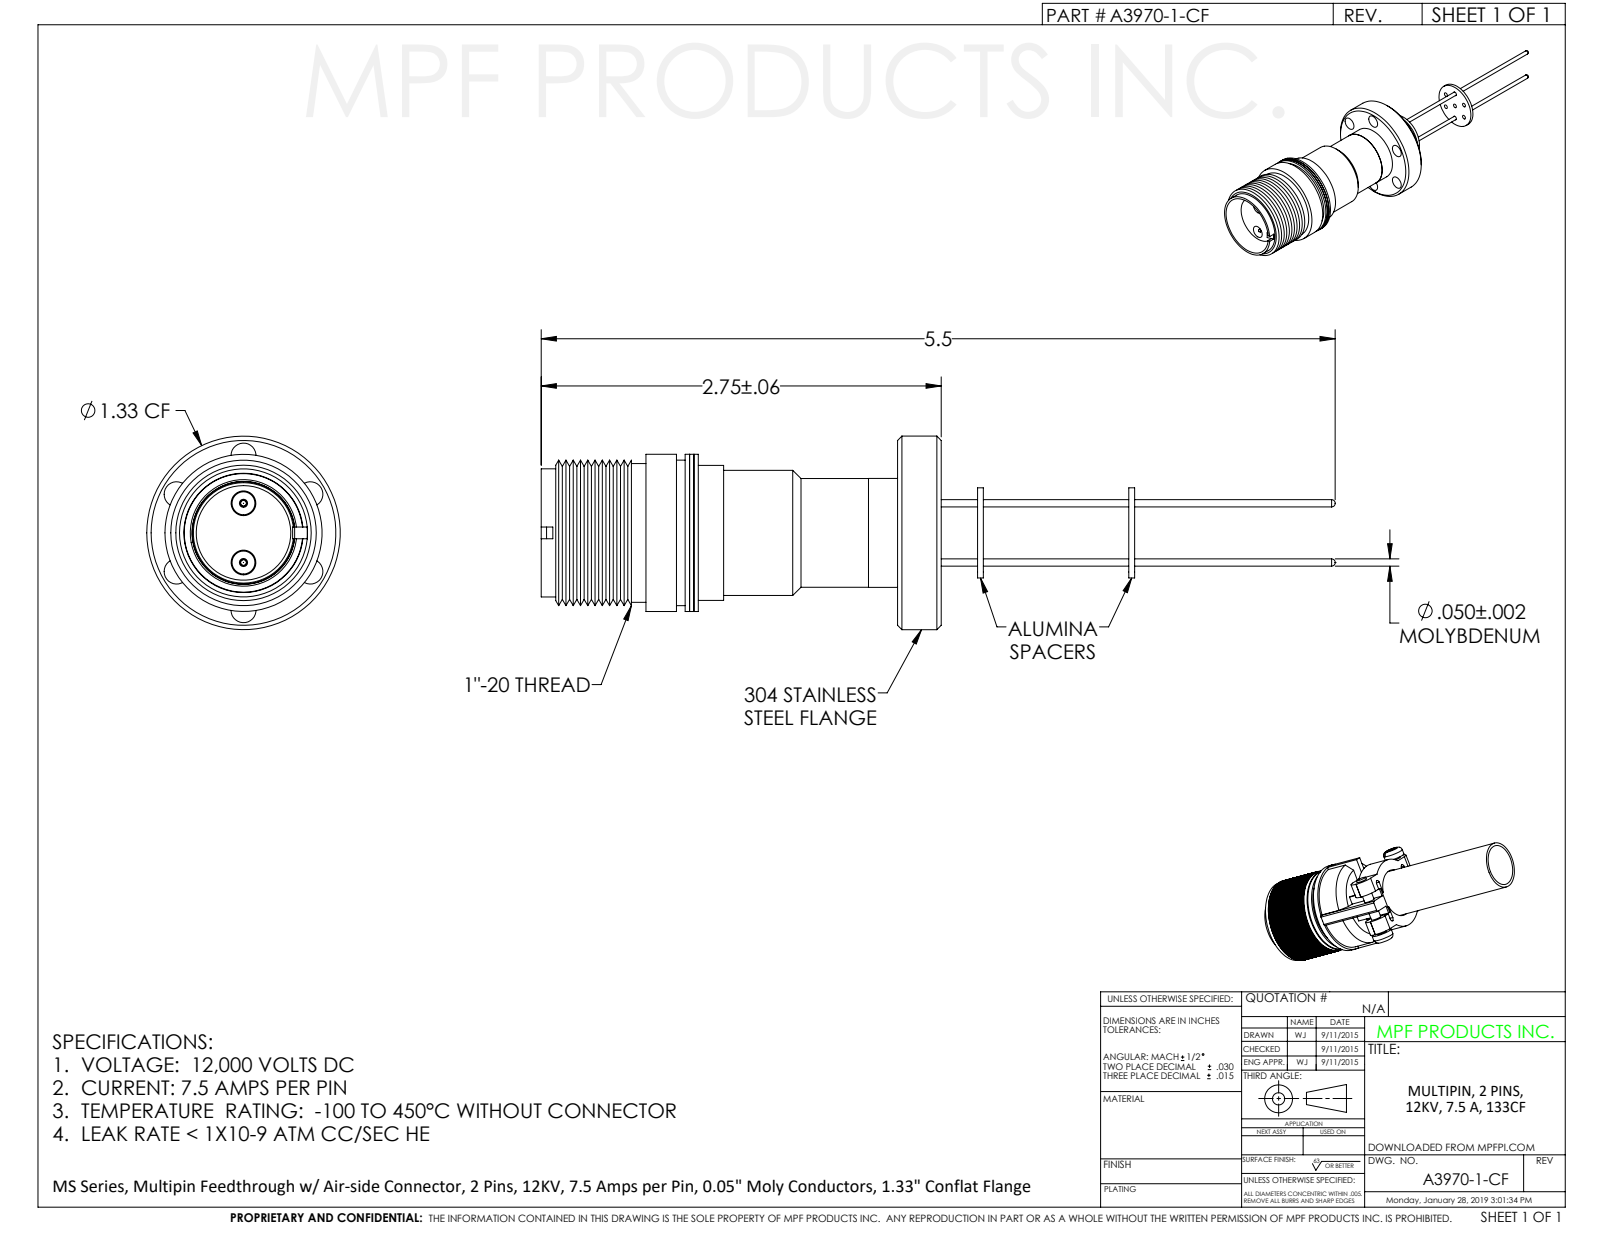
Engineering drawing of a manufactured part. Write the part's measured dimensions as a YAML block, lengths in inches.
part_name: "A3970-1-CF"
step_written_by: "SolidWorks 2012 (CONFIG_CONTROL_DESIGN)"
units: inches
bodies: {solids: 1, faces: 254, planar: 41, cylindrical: 119, other: 94}
overall_size: [5.464, 1.33, 1.33]
volume: 1.214
surface_area: 28.89
round_holes:
  - {diameter: 0.172, count: 6}
  - {diameter: 0.036, count: 5}
  - {diameter: 0.054, count: 2}
  - {diameter: 0.056, count: 2}
  - {diameter: 0.152, count: 2}
  - {diameter: 0.63, count: 1}
  - {diameter: 0.687, count: 1}
  - {diameter: 0.725, count: 1}
  - {diameter: 0.791, count: 1}
  - {diameter: 0.8, count: 1}
  - {diameter: 0.82, count: 1}
  - {diameter: 0.845, count: 1}
round_bosses_or_shafts:
  - {diameter: 0.117, count: 2}
  - {diameter: 0.05, count: 2}
  - {diameter: 0.04, count: 2}
  - {diameter: 1.33, count: 1}
  - {diameter: 1.08, count: 1}
  - {diameter: 1, count: 1}
  - {diameter: 0.954, count: 1}
  - {diameter: 0.928, count: 1}
face_to_face_distances: [0.285, 0.758, 1.043, 1.908, 1.15, 0.865, 1.328, 0.569, 0.284, 0.581]
hole_center_spacings: [0.204, 0.531, 0.464, 0.657, 0.328, 0.92, 0.352, 0.464]
